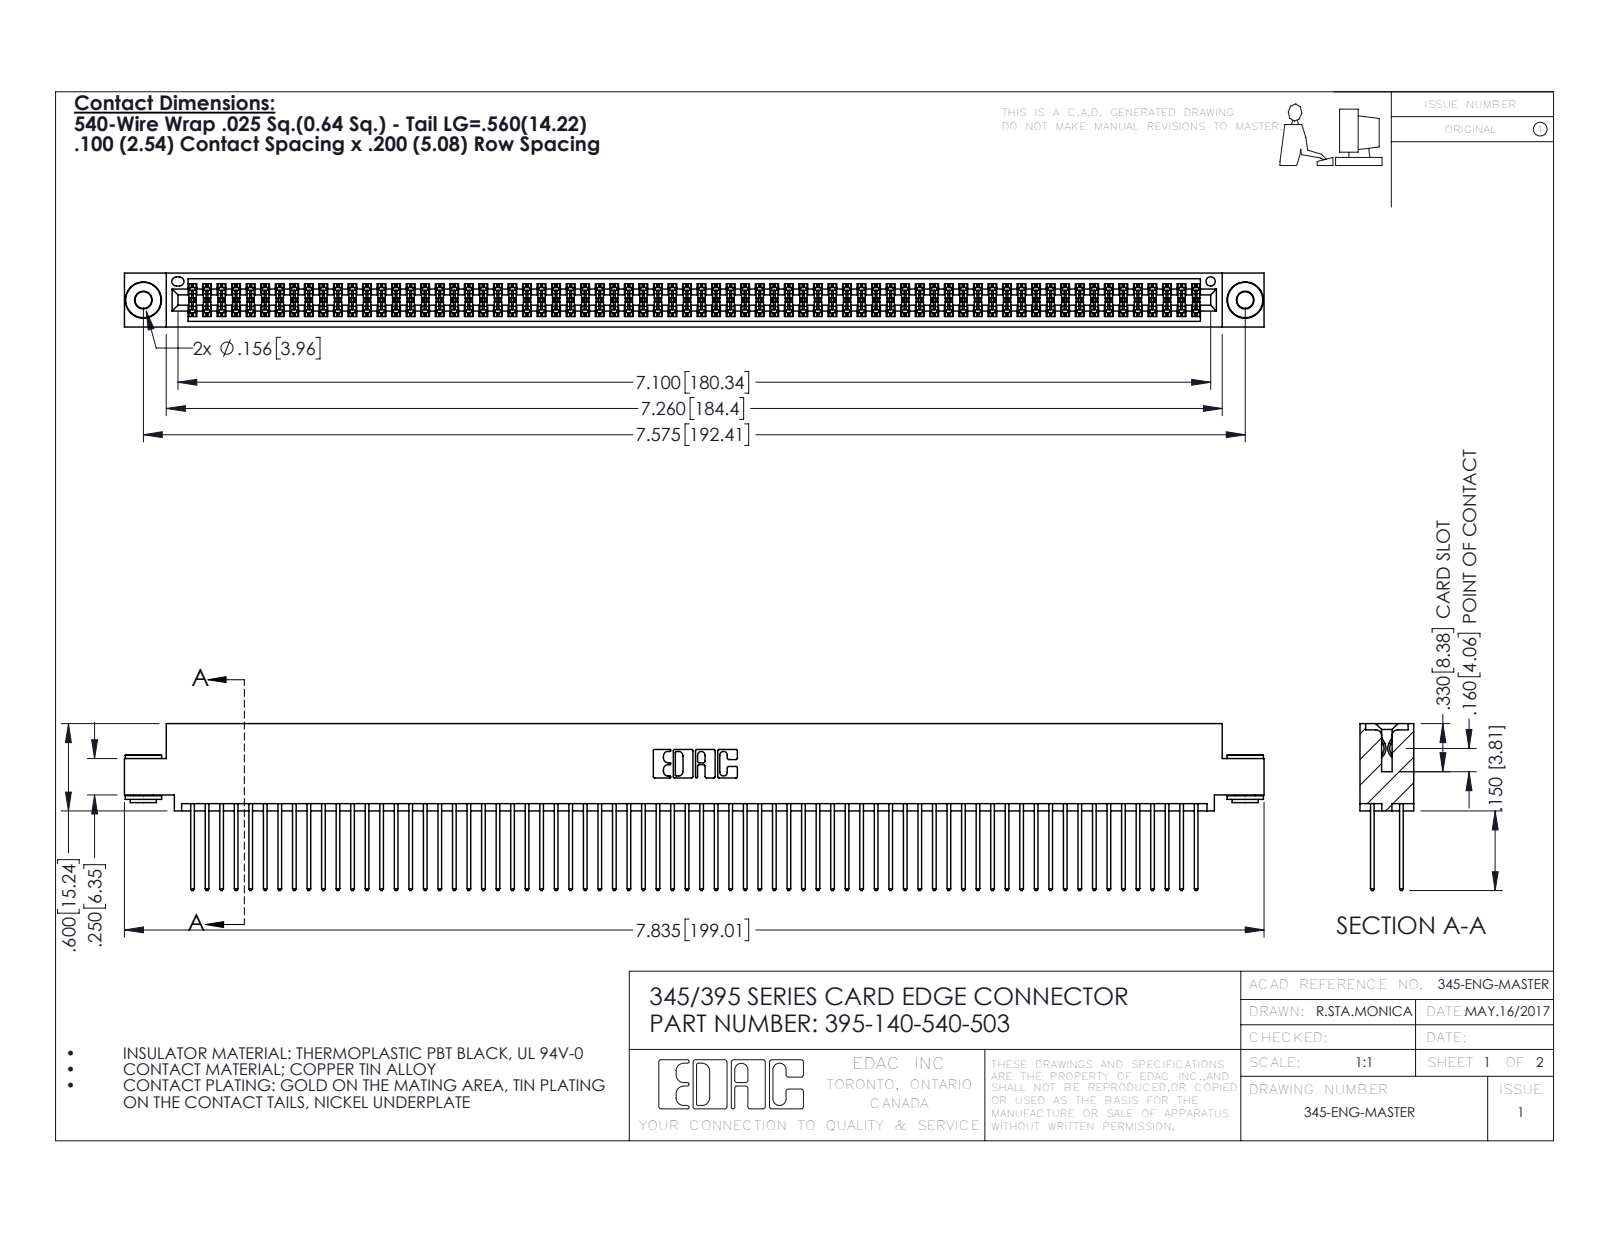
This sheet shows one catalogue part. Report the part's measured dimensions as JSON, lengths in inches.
{"part_name": "345-250-002_345-250-002-102; 395-140-540-503; 345 Part_0.110 Offset - 0.156 Dia-TH; 345-292-001_345-293-140", "step_written_by": "SolidWorks 2016 (CONFIG_CONTROL_DESIGN)", "units": "inches", "bodies": {"solids": 143, "faces": 7168, "planar": 4714, "cylindrical": 2446, "other": 8}, "overall_size": [7.835, 1.147, 0.37], "volume_in3": 1.225, "surface_area_in2": 51.1, "round_holes": [[0.116, 2], [0.156, 2], [0.064, 1]], "round_bosses_or_shafts": [[0.25, 2], [0.18, 2], [0.136, 2]], "partial_cylinders_radius": [[0.006, 210], [0.01, 140], [0.01, 22], [0.007, 6], [0.031, 6], [0.026, 3], [0.014, 2], [0.019, 2]], "face_to_face_distances": [0.072, 0.298, 0.2, 0.025, 0.098, 0.272, 0.225, 0.37, 0.175, 0.149], "hole_center_spacings": [0.27, 7.339, 7.575]}
